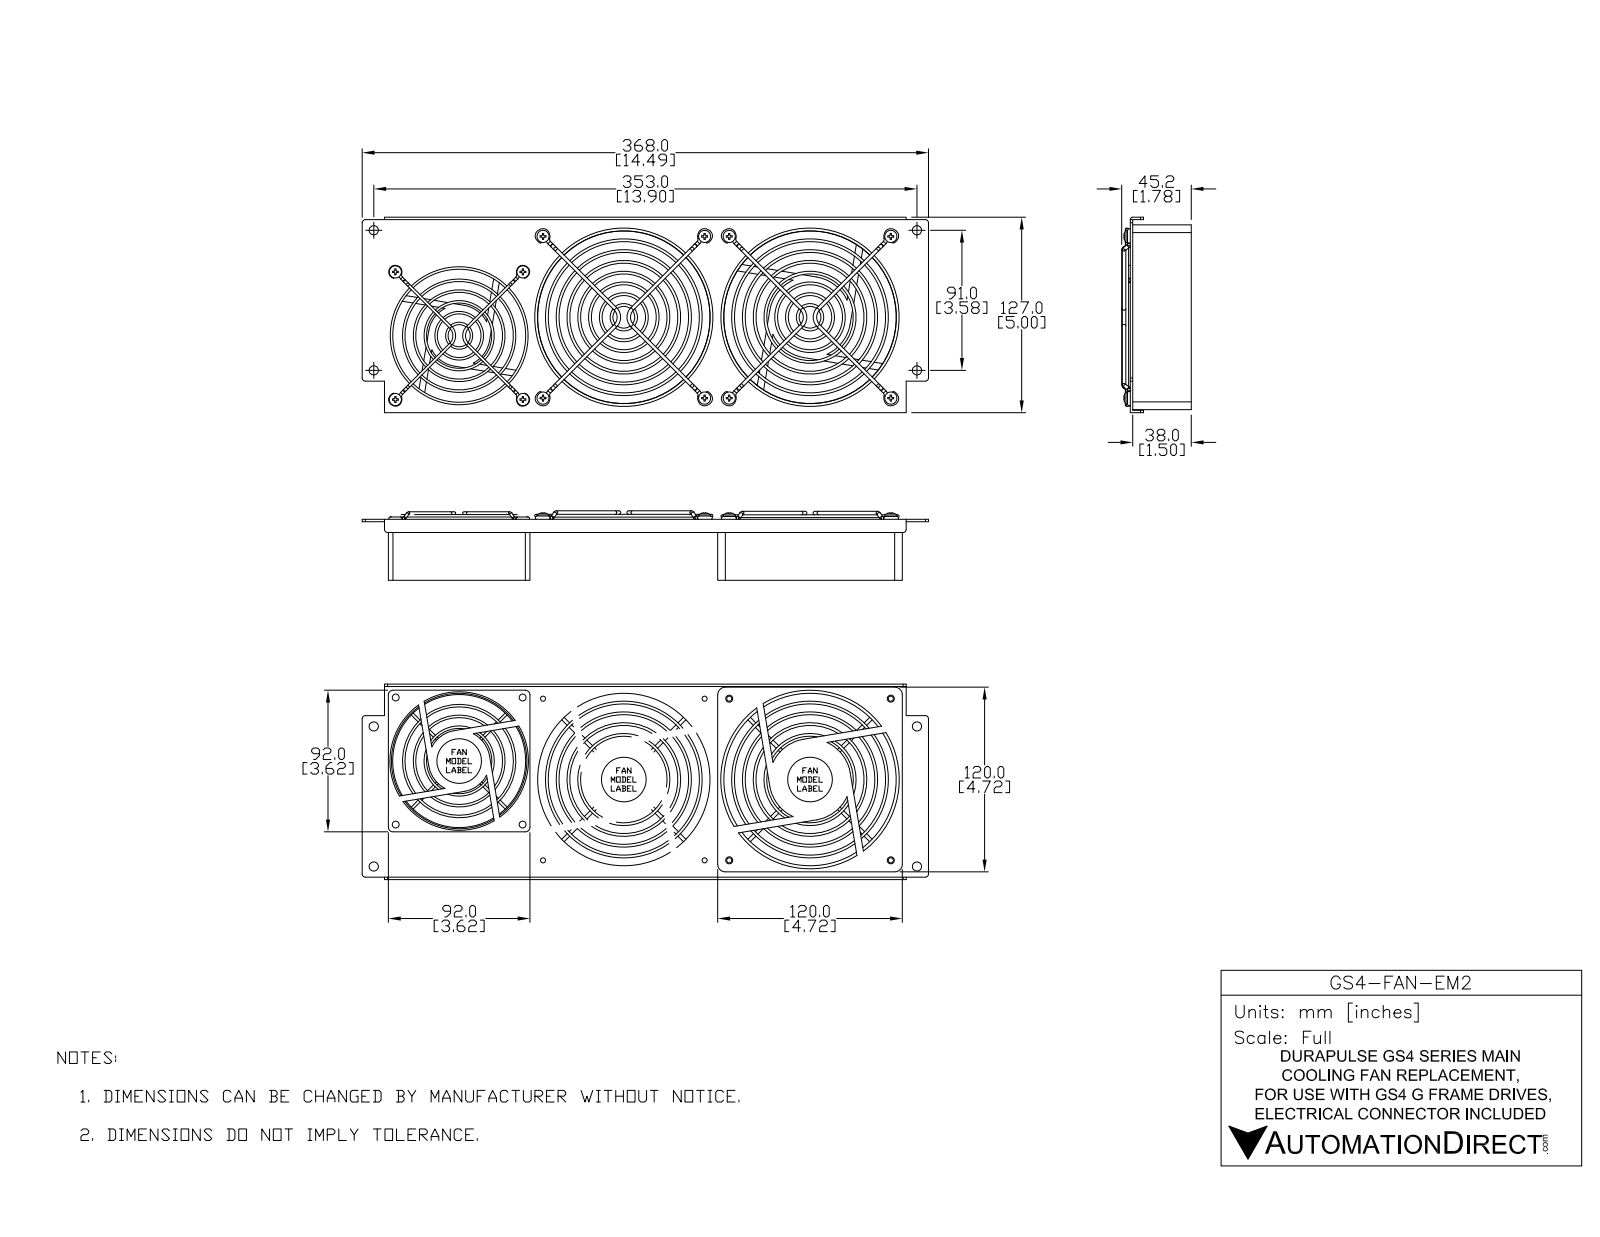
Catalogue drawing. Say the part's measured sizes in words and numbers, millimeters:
The part is named "GS4-FAN-EM2". Its 3-D file was written by "SolidWorks 2015 (AUTOMOTIVE_DESIGN)". It is 0 solids with 335 faces: 62 planar, 103 cylindrical and 170 other. Overall it measures 368 by 127 by 45.15 millimeters. Round holes: 2 of diameter 116, 1 of diameter 90. Round bosses or shafts: 4 of diameter 6, 2 of diameter 2.3. Partial cylindrical surfaces (rounded edges, fillets, slot ends): 22 of radius 1.15, 10 of radius 0.9, 8 of radius 5, 6 of radius 2, 4 of radius 3, 2 of radius 3.95, 2 of radius 26.5, 1 of radius 1.6. The main face-to-face distances are 1.6, 38, 39.6, 48.41, 4.61, 120, 2, 43.8, 119.31, 19.97. The hole center spacings are 107.67, 121, 228.32.
